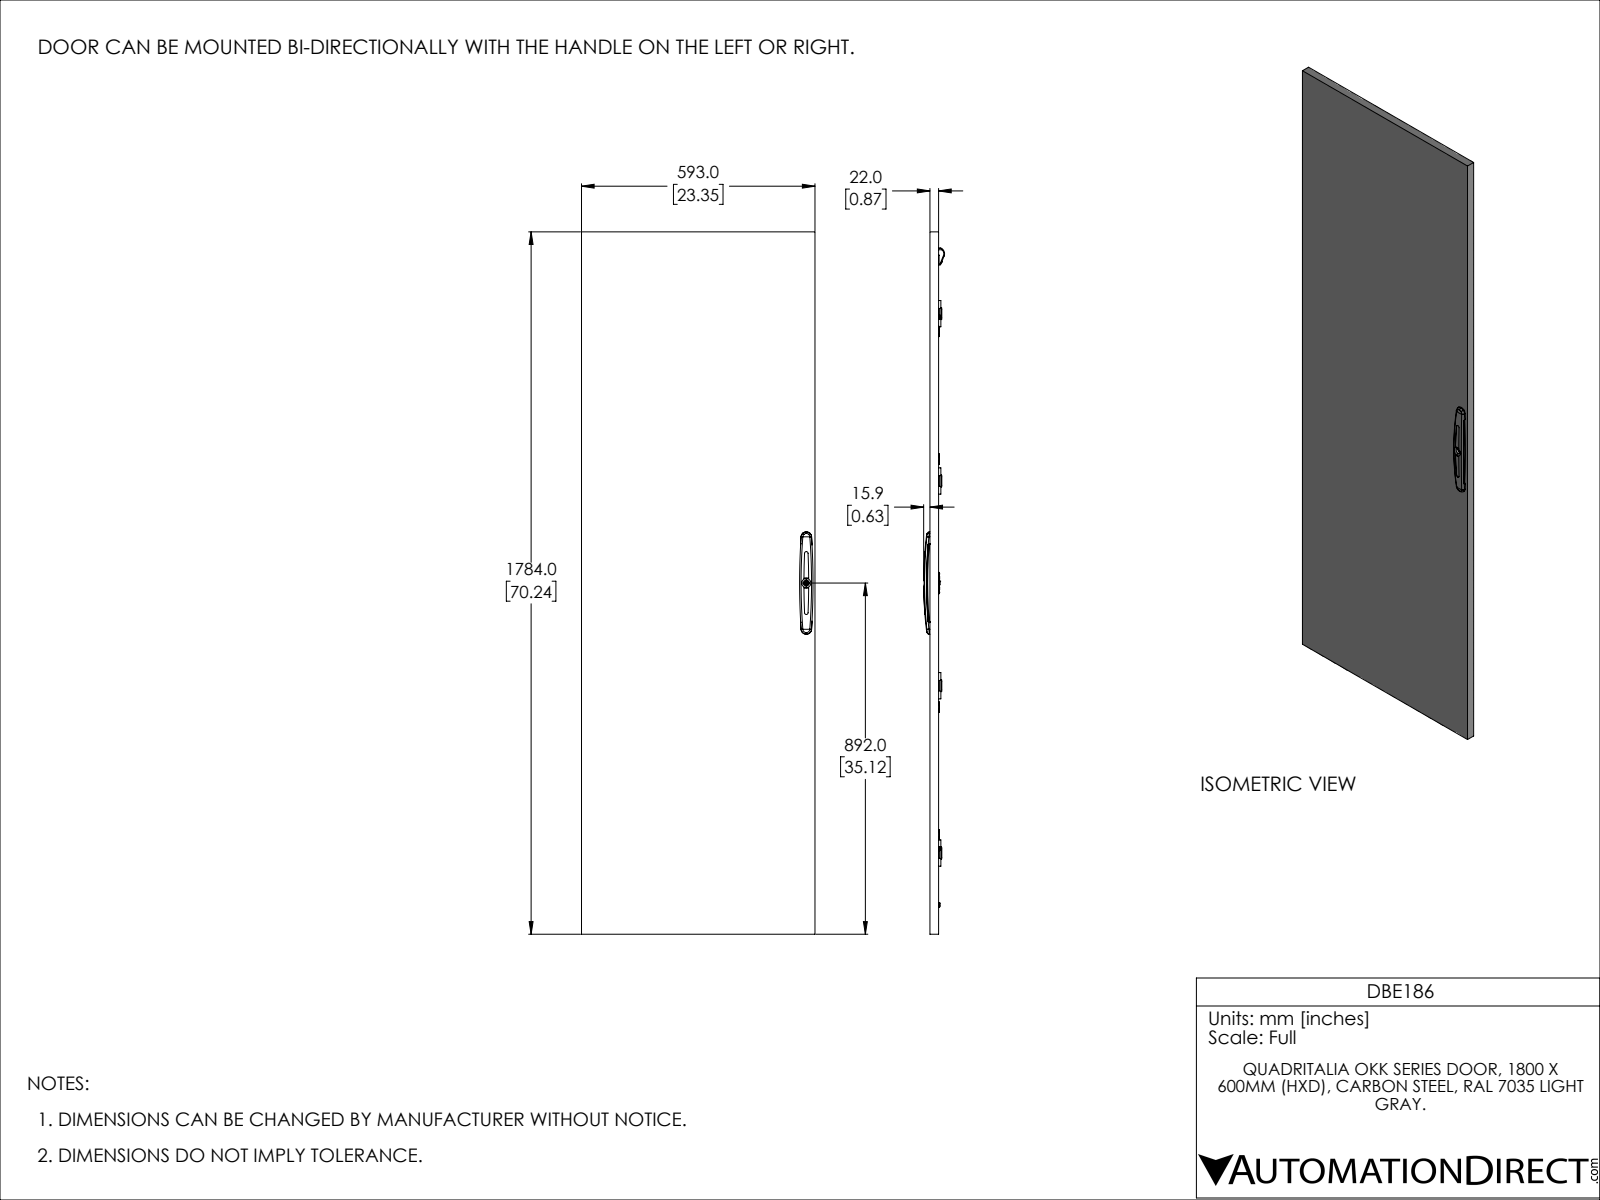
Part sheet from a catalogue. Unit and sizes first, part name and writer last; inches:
Units: inches
Overall size (bounding box): 70.236 × 23.346 × 2.091
Round holes (diameter × count): ⌀0.167 ×136, ⌀0.354 ×18, ⌀0.01 ×8, ⌀0.197 ×8, ⌀0.194 ×6, ⌀0.194 ×4, ⌀0.244 ×4, ⌀0.276 ×4, ⌀0.205 ×3, ⌀0.134 ×2, ⌀0.169 ×2, ⌀0.173 ×2
Round bosses / shafts (diameter × count): ⌀0.276 ×23, ⌀0.236 ×19, ⌀0.283 ×10, ⌀0.193 ×8, ⌀0.394 ×2, ⌀0.315 ×2, ⌀0.157 ×2, ⌀0.626 ×1
Partial cylindrical surfaces — rounded edges, fillets, slot ends (radius × count): R0.012 ×74, R0.039 ×70, R0.059 ×36, R0.02 ×33, R0.098 ×28, R0.177 ×16, R0.079 ×15, R0.016 ×8
Main face-to-face distances: 0.079, 0.059, 0.728, 0.787, 0.669, 18.11, 0.866, 23.268, 0.138, 0.807
Hole centre spacings: 0.394, 0.984, 1.969, 16.732, 32.516, 34.896, 37.205, 0.787
Volume: 208.5 in³ · Surface area: 5 141 in²
Bodies: 85 solids, 3167 faces (1517 planar, 1126 cylindrical, 524 other)
Part name (STEP PRODUCT): DBE186
STEP written by: SolidWorks 2021 (CONFIG_CONTROL_DESIGN)
